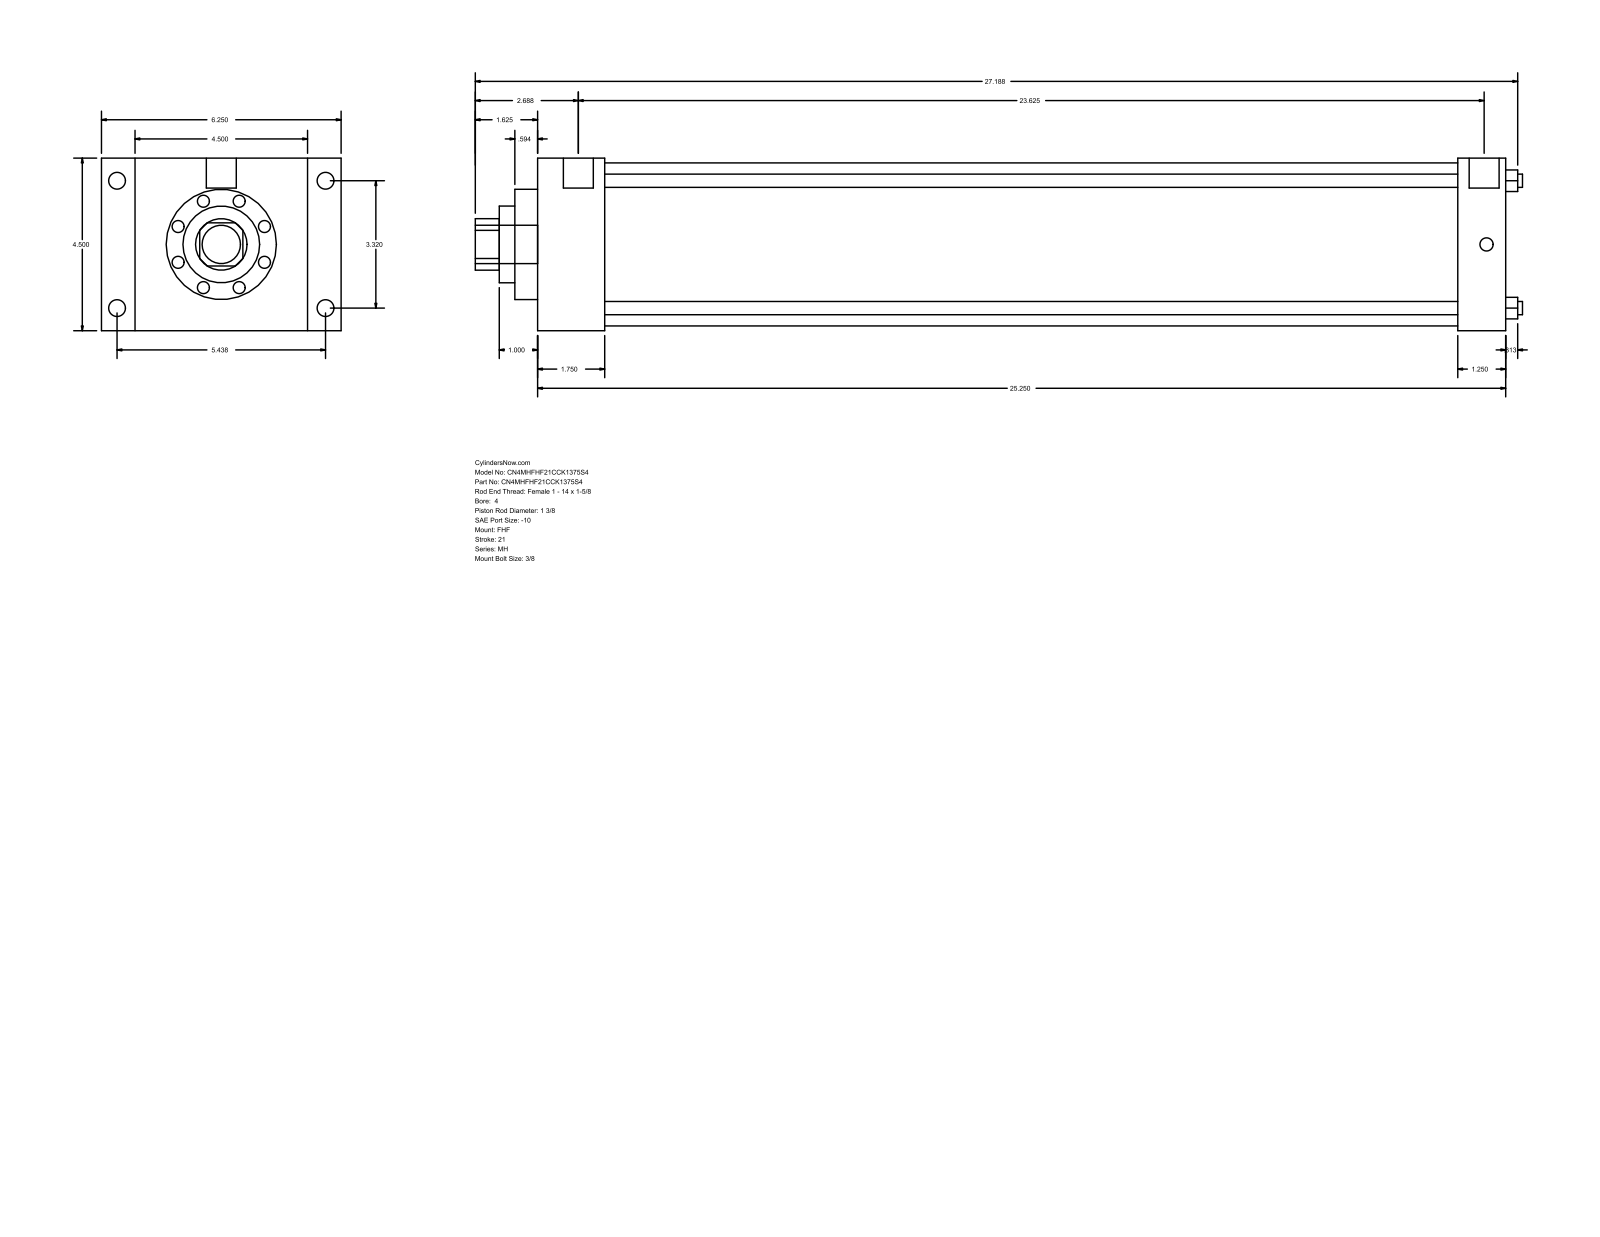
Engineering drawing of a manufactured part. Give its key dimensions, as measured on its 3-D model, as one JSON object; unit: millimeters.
{"part_name": "MH_FHF__0400_1.375", "step_written_by": "GSSL Pune (CONFIG_CONTROL_DESIGN)", "units": "millimeters", "bodies": {"solids": 0, "faces": 90, "planar": 61, "cylindrical": 29, "other": 0}, "overall_size": [693.74, 158.75, 114.3], "round_holes": [[8.76, 4], [34.92, 1], [50.8, 1], [73.03, 1], [107.95, 1]], "round_bosses_or_shafts": [[11.13, 4], [8.73, 4], [19.84, 2], [25.4, 1]], "partial_cylinders_radius": [[17.06, 1]], "face_to_face_distances": [114.3, 641.35, 44.45, 596.9, 22.23, 136.53, 158.76, 609.61, 565.16, 31.74], "hole_center_spacings": [59.62, 84.32, 119.25]}
